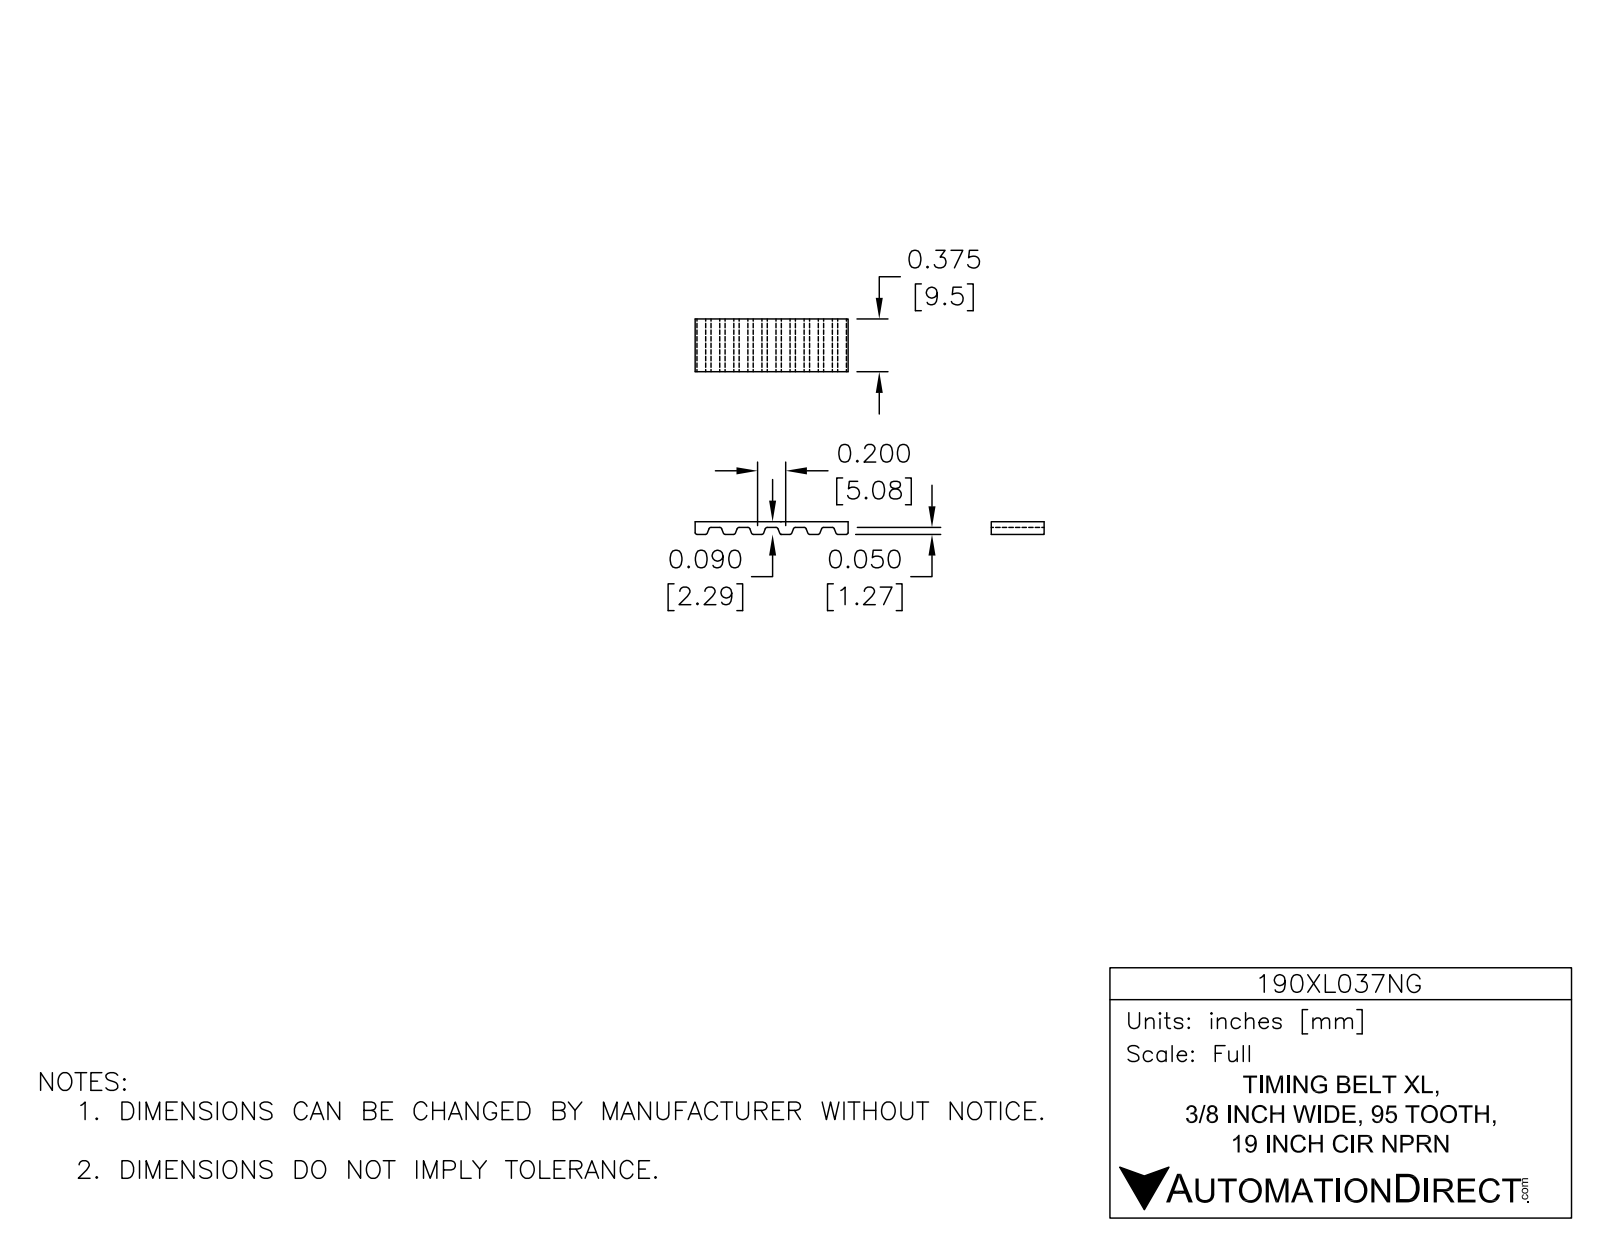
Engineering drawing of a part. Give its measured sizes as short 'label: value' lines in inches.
name: 190XL037NG
written by: SolidWorks 2014 (AUTOMOTIVE_DESIGN)
unit: in
bodies: 1 solid, 800 faces (338 planar, 462 cylindrical, 0 other)
size: 7.788 × 3 × 0.375
volume: 0.387 in³; area: 18.19 in²
rounds: 380× R0.015, 2× R1.46, 2× R1.5
face distances: 3, 0.04, 2.96, 0.375, 2.92, 0.179, 1.073, 0.09, 2.91, 0.05
